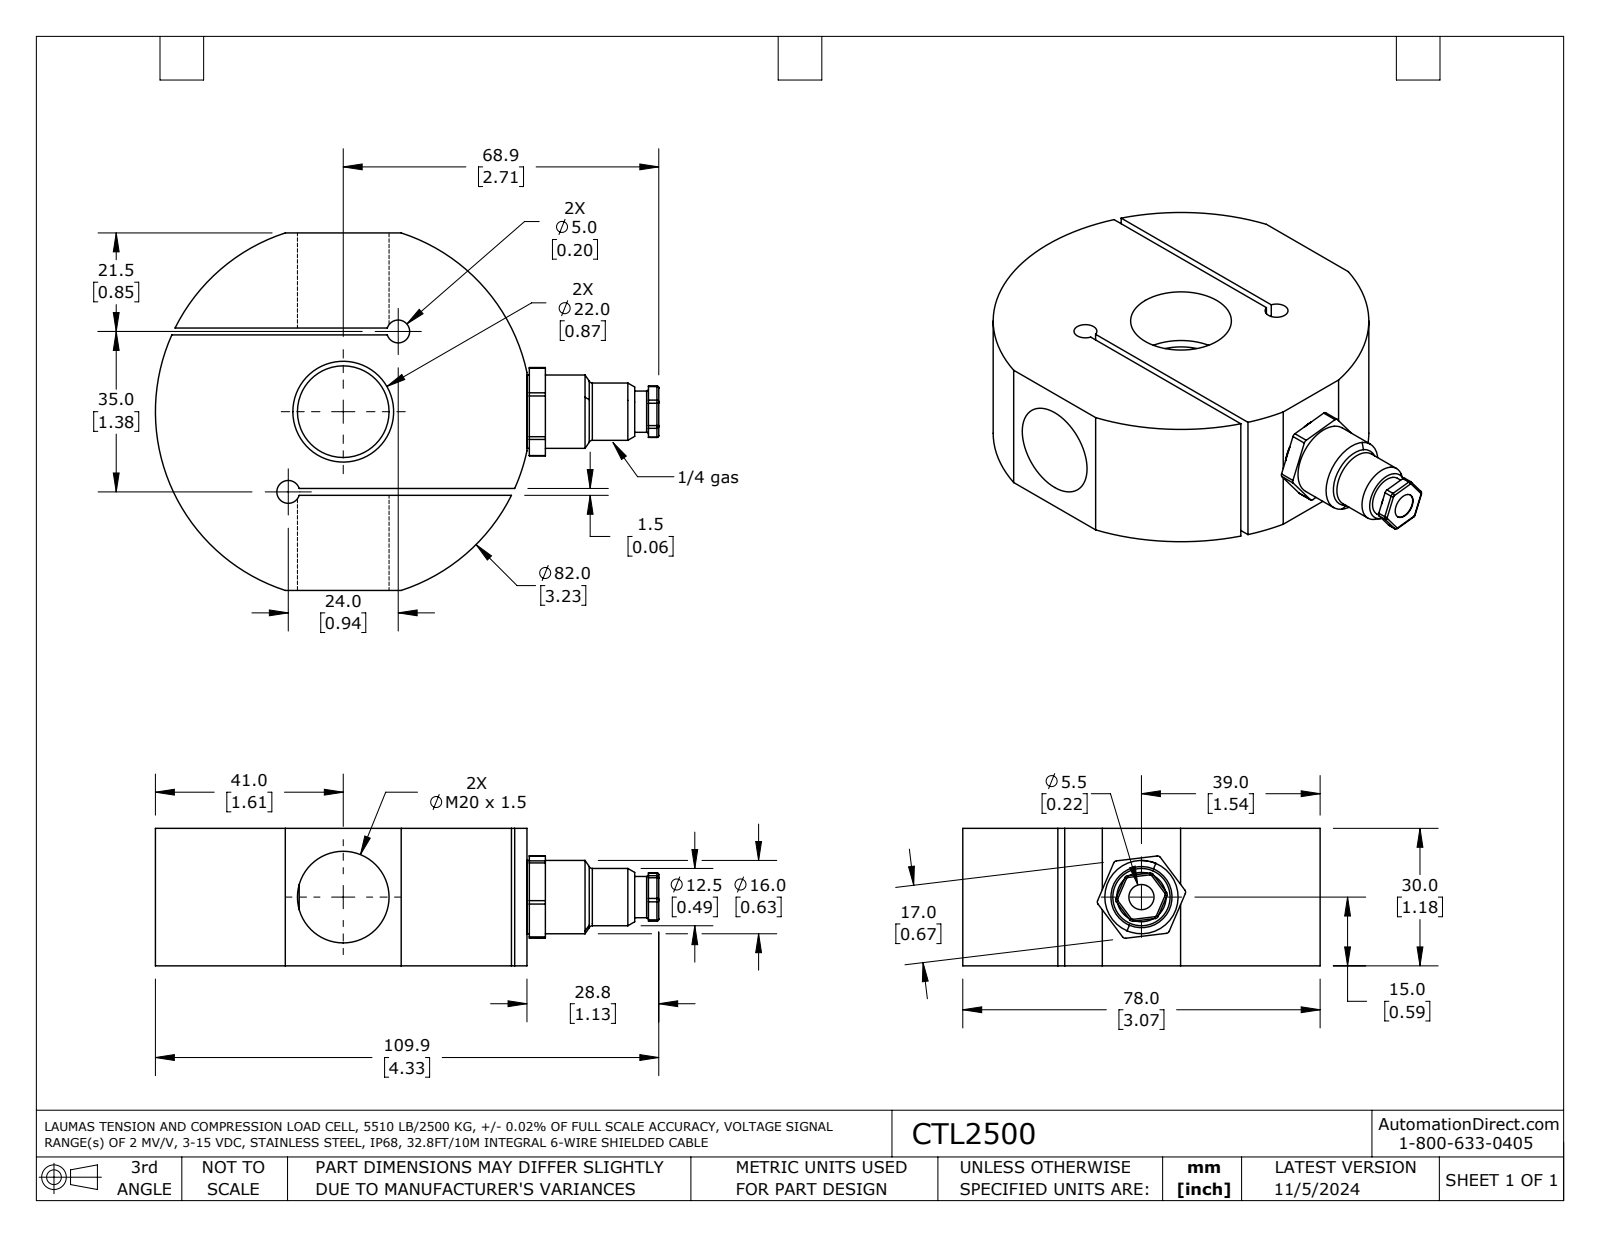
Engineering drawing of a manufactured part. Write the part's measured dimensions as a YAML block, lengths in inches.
part_name: "CTL2500"
step_written_by: "SolidWorks 2021 (AUTOMOTIVE_DESIGN)"
units: inches
bodies: {solids: 2, faces: 102, planar: 32, cylindrical: 51, other: 19}
overall_size: [4.326, 3.071, 1.181]
volume: 7.894
surface_area: 45.96
round_holes:
  - {diameter: 0.197, count: 2}
  - {diameter: 0.217, count: 1}
  - {diameter: 0.551, count: 1}
  - {diameter: 0.787, count: 1}
  - {diameter: 0.866, count: 1}
round_bosses_or_shafts:
  - {diameter: 0.63, count: 1}
  - {diameter: 0.492, count: 1}
  - {diameter: 0.354, count: 1}
partial_cylinders:
  - {radius: 0.03, count: 12}
  - {radius: 0.016, count: 6}
  - {radius: 1.614, count: 1}
face_to_face_distances: [1.181, 0.059, 1.378, 1.319, 1.437, 0.817, 0.876, 2.195, 2.254, 0.551]
hole_center_spacings: [0.835, 1.671]
